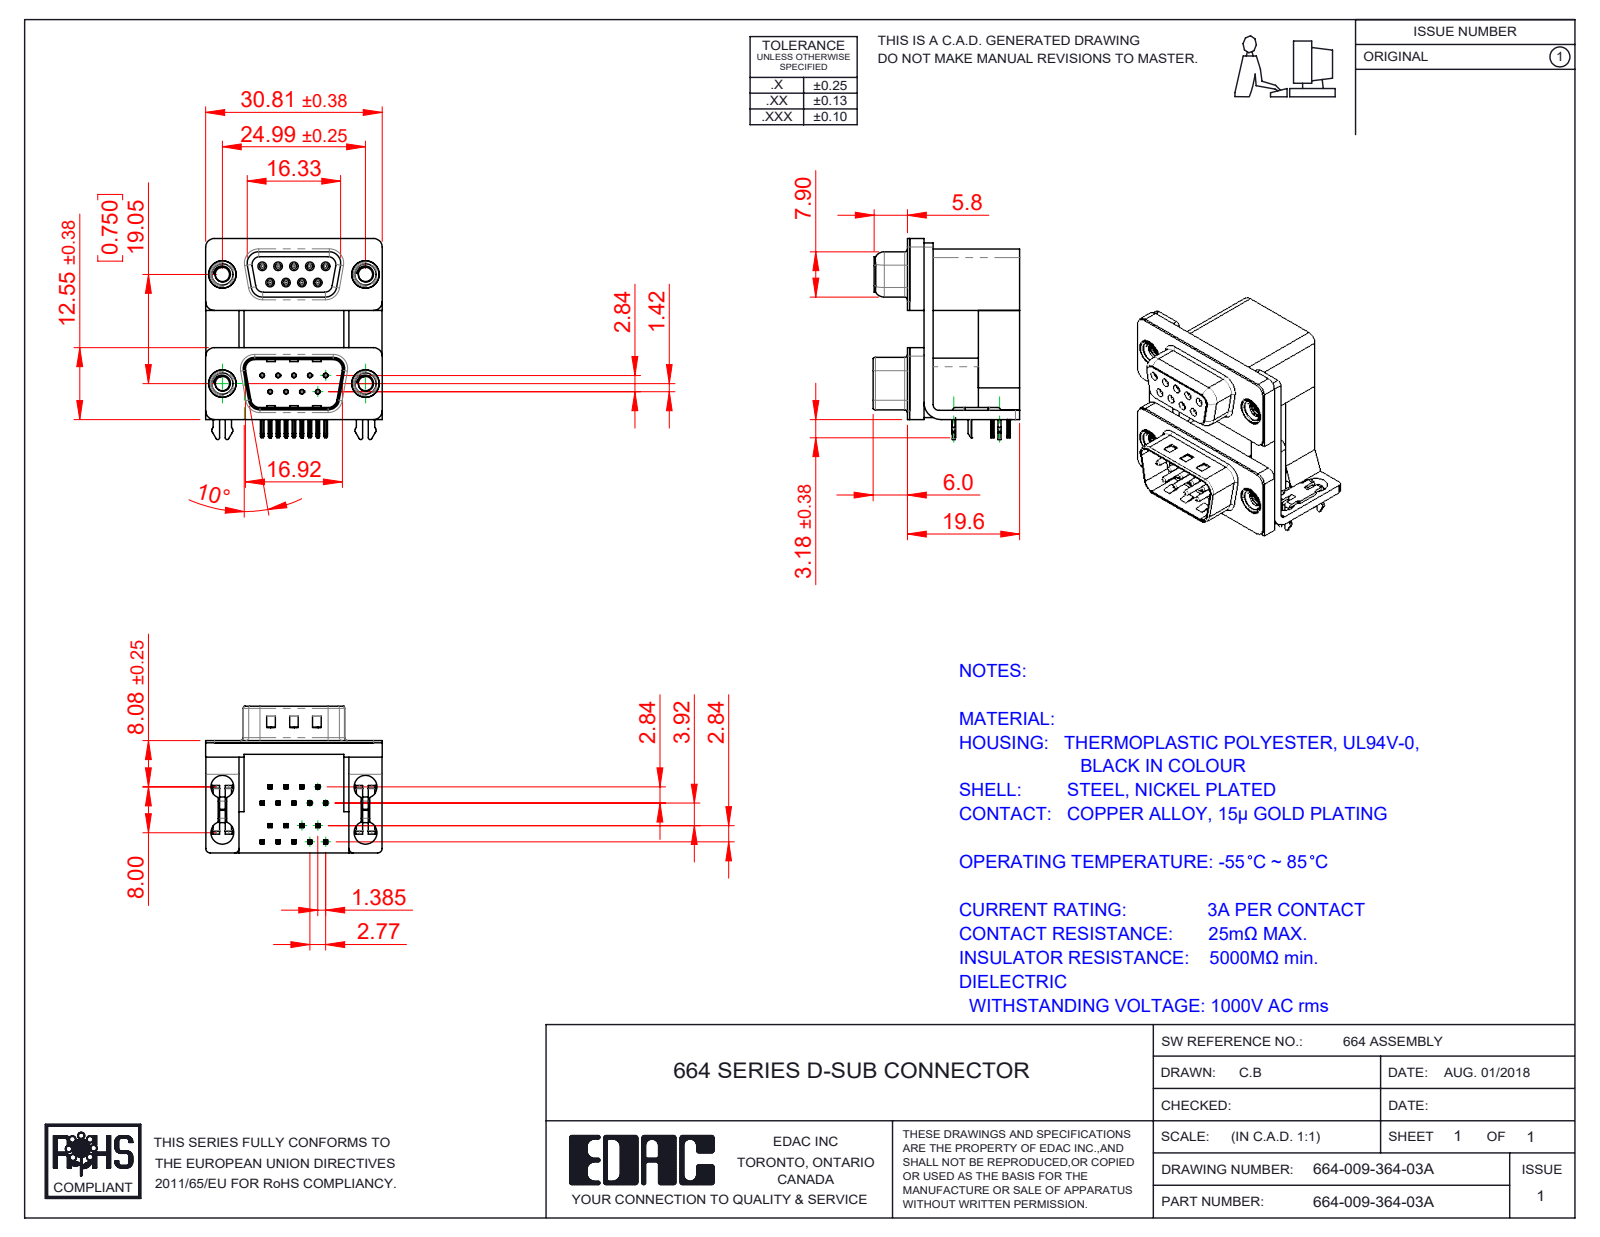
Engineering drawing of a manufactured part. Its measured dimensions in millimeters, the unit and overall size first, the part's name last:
Units: millimetres
Overall size (bounding box): 35.1 × 30.81 × 25.6
Round holes (diameter × count): ⌀0.8 ×18, ⌀0.35 ×9, ⌀0.9 ×9, ⌀4 ×8, ⌀2.5 ×4, ⌀3.5 ×4, ⌀4.8 ×4, ⌀5 ×4
Round bosses / shafts (diameter × count): ⌀1.2 ×9, ⌀0.75 ×9, ⌀4.9 ×4, ⌀4.75 ×4, ⌀3.9 ×4
Partial cylindrical surfaces — rounded edges, fillets, slot ends (radius × count): R0.1 ×74, R0.25 ×46, R0.15 ×36, R0.12 ×18, R0.35 ×18, R0.5 ×16, R1.5 ×13, R0.75 ×10
Main face-to-face distances: 0.4, 2.5, 16.7, 19.2, 7.2, 9.5, 12, 1.6, 19.6, 12.4
Hole centre spacings: 3.16, 2.77, 19.25, 19.05, 5.54, 19.84, 16.27, 21.93
Volume: 10 769 mm³ · Surface area: 12 804 mm²
Bodies: 31 solids, 2685 faces (1365 planar, 753 cylindrical, 567 other)
Part name (STEP PRODUCT): 664 Shell Receptacle_09 Contacts; 664 Mounting Bracket_2ProngM; 664 Contact Top Upper_M; 664 2 Prong Board Lock_3 (+8 more)
STEP written by: SolidWorks 2020 (CONFIG_CONTROL_DESIGN)
